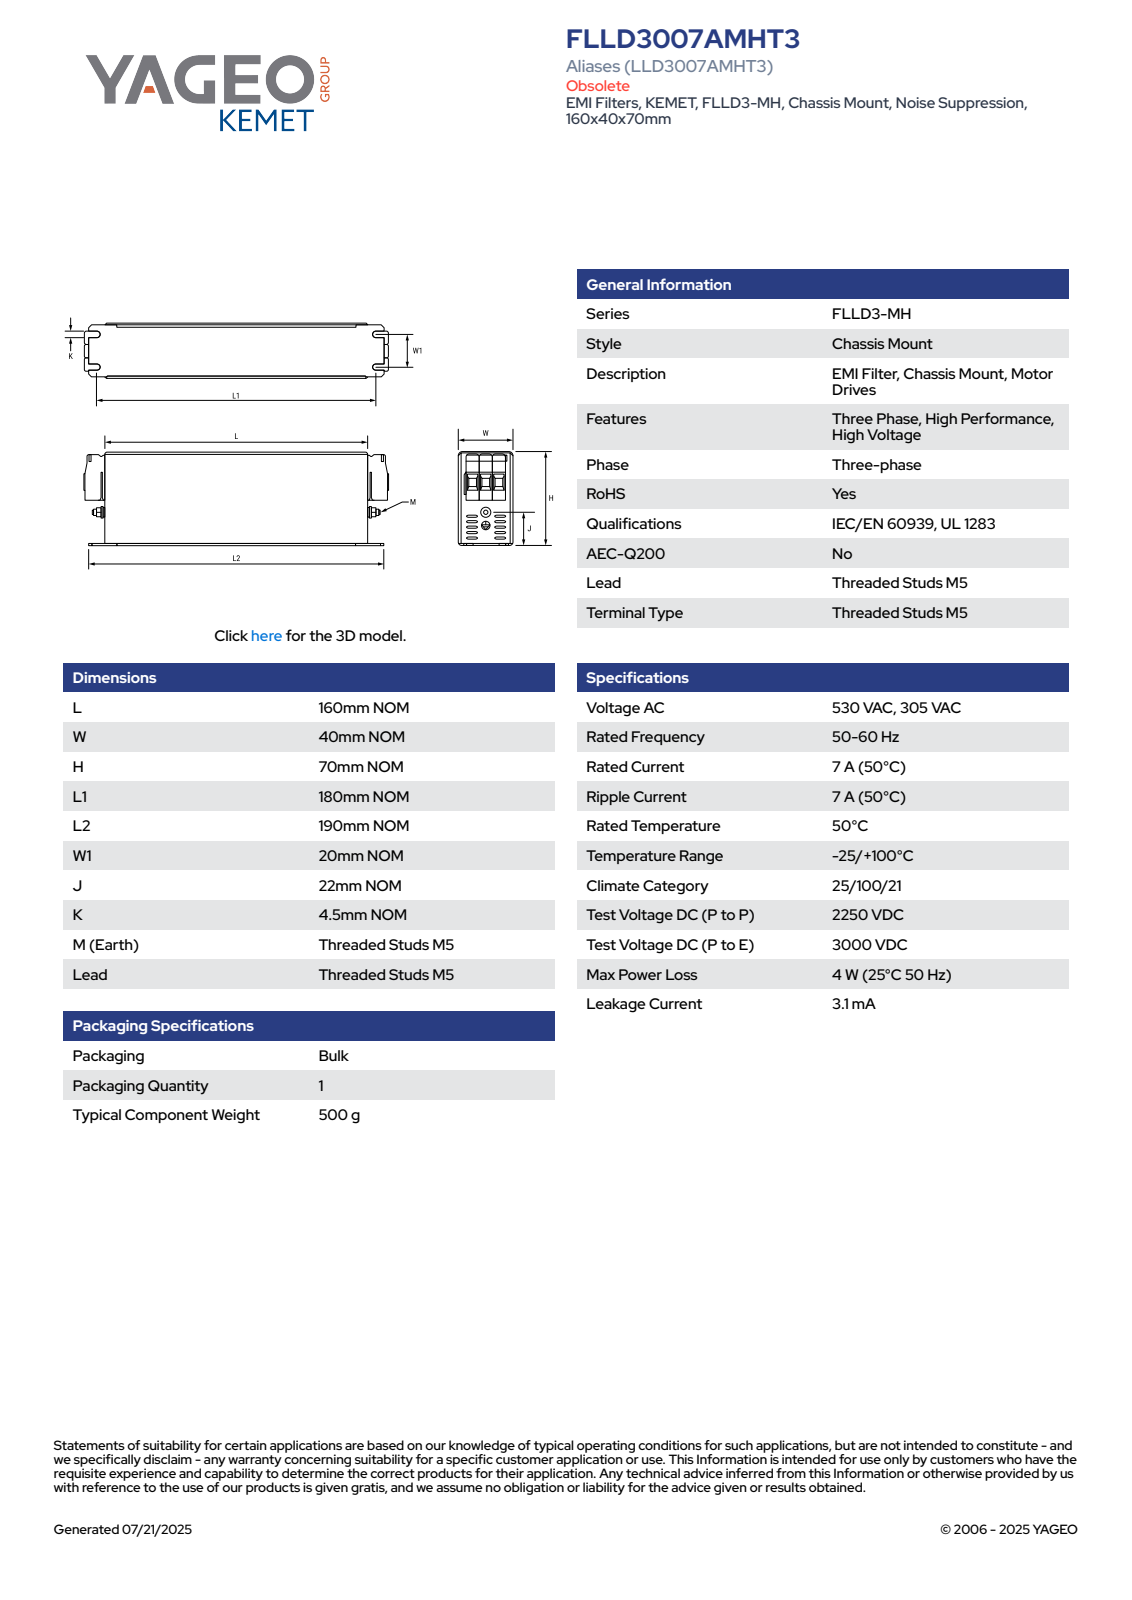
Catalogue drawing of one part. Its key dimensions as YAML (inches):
part_name: "EFC_KFLLD3MH_L160W40H70L1180L2190W120"
step_written_by: "SolidWorks 2014 (AUTOMOTIVE_DESIGN)"
units: inches
bodies: {solids: 4, faces: 153, planar: 117, cylindrical: 32, other: 4}
overall_size: [7.48, 2.756, 1.575]
volume: 27.76
surface_area: 70.36
round_bosses_or_shafts:
  - {diameter: 0.315, count: 1}
  - {diameter: 0.236, count: 1}
  - {diameter: 0.197, count: 1}
partial_cylinders:
  - {radius: 0.157, count: 8}
  - {radius: 0.079, count: 4}
  - {radius: 0.089, count: 4}
face_to_face_distances: [1.575, 2.756, 0.315, 0.039, 6.299, 0.354, 2.717, 6.614, 0.394, 0.276]
